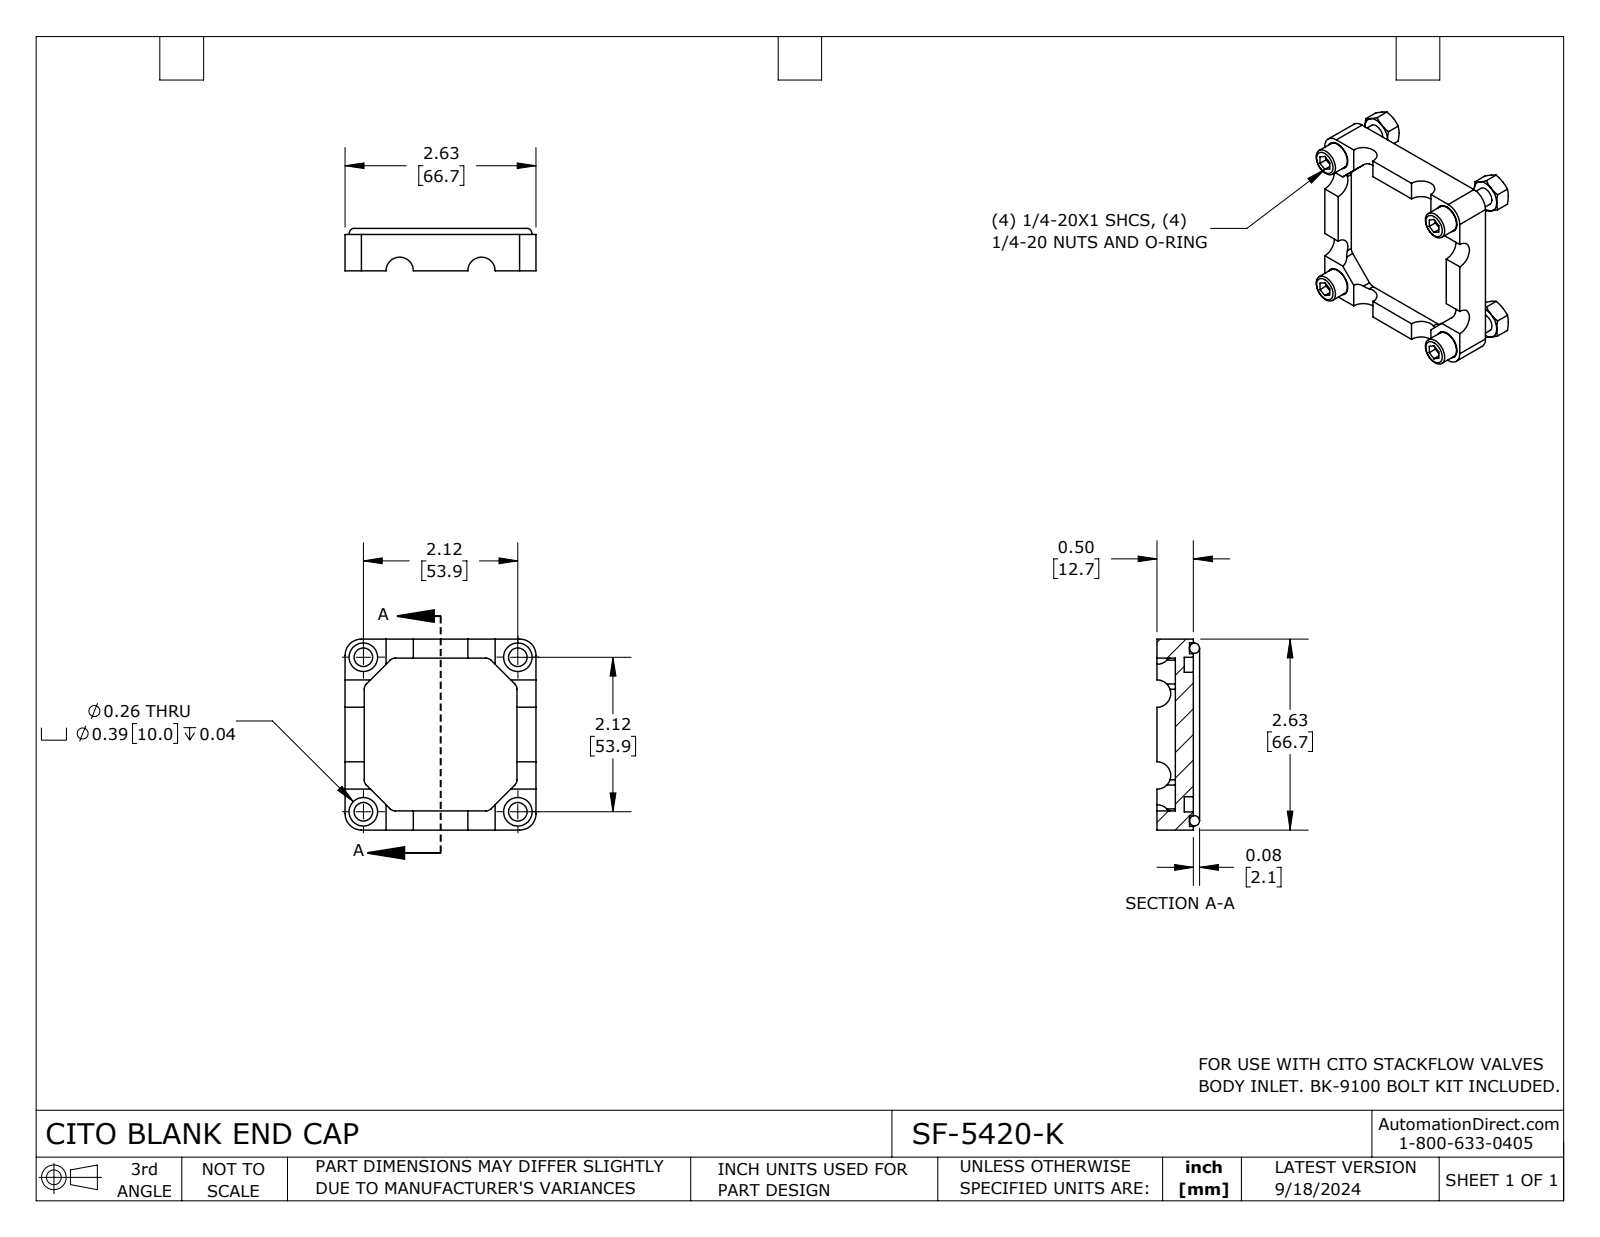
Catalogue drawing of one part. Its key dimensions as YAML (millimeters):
part_name: "SF-5420-K"
step_written_by: "SolidWorks 2023 (CONFIG_CONTROL_DESIGN)"
units: millimeters
bodies: {solids: 2, faces: 96, planar: 36, cylindrical: 56, other: 4}
overall_size: [66.7, 66.7, 14.8]
volume: 33450
surface_area: 17500
round_holes:
  - {diameter: 6.5, count: 4}
  - {diameter: 10, count: 4}
  - {diameter: 54, count: 1}
  - {diameter: 64.1, count: 1}
round_bosses_or_shafts:
  - {diameter: 56.5, count: 1}
  - {diameter: 43.4, count: 1}
partial_cylinders:
  - {radius: 2.5, count: 8}
  - {radius: 0.8, count: 6}
  - {radius: 4.7, count: 4}
  - {radius: 5.7, count: 4}
  - {radius: 19.2, count: 1}
face_to_face_distances: [6.3, 66.7, 6.4, 12.7, 9.5, 3.1, 3.2, 11.3, 4.9, 1.8]
hole_center_spacings: [38.2, 53.9, 76.3]
